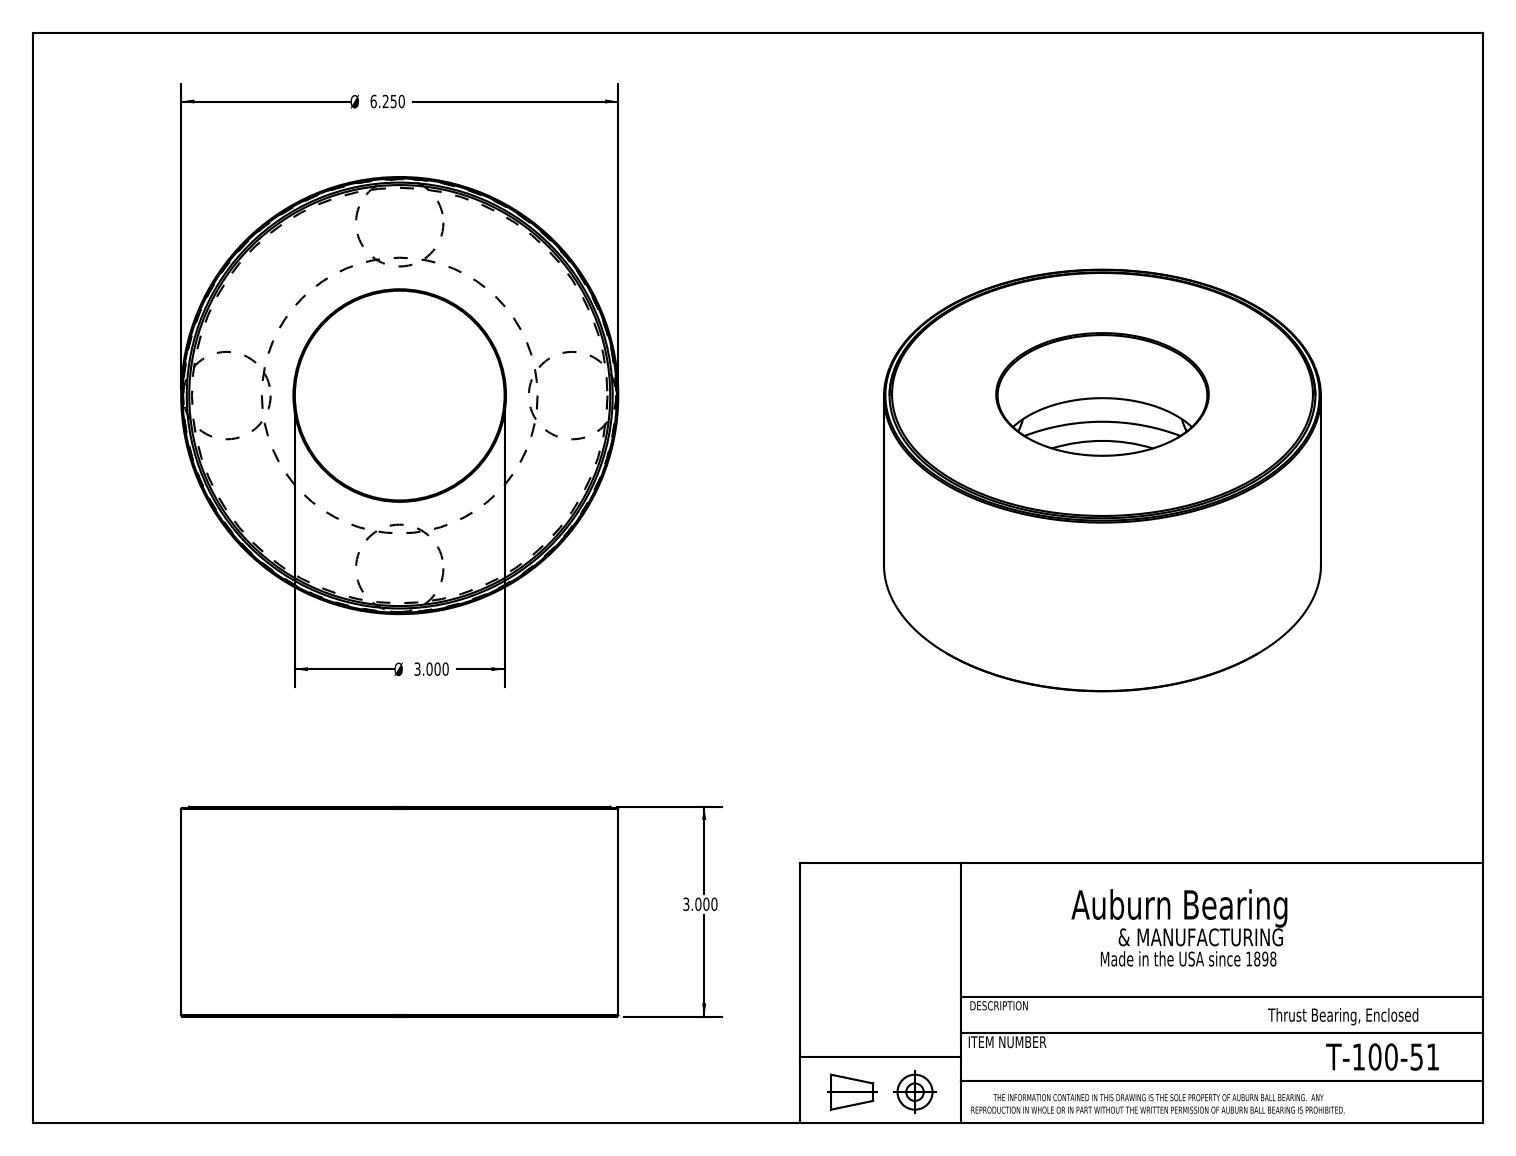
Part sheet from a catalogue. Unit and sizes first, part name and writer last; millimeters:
Units: millimetres
Overall size (bounding box): 158.8 × 158.8 × 76.2
Round holes (diameter × count): ⌀76.2 ×1, ⌀154.7 ×1, ⌀157.7 ×1
Round bosses / shafts (diameter × count): ⌀158.8 ×1, ⌀157.4 ×1
Main face-to-face distances: 76.2, 28.6, 47.6, 19.1, 75.3, 46.7, 27.7, 0.9, 75.8, 47.2
Volume: 849 800 mm³ · Surface area: 165 700 mm²
Bodies: 6 solids, 28 faces (9 planar, 7 cylindrical, 12 other)
Part name (STEP PRODUCT): T-100-51
STEP written by: SolidWorks 2016 (CONFIG_CONTROL_DESIGN)
